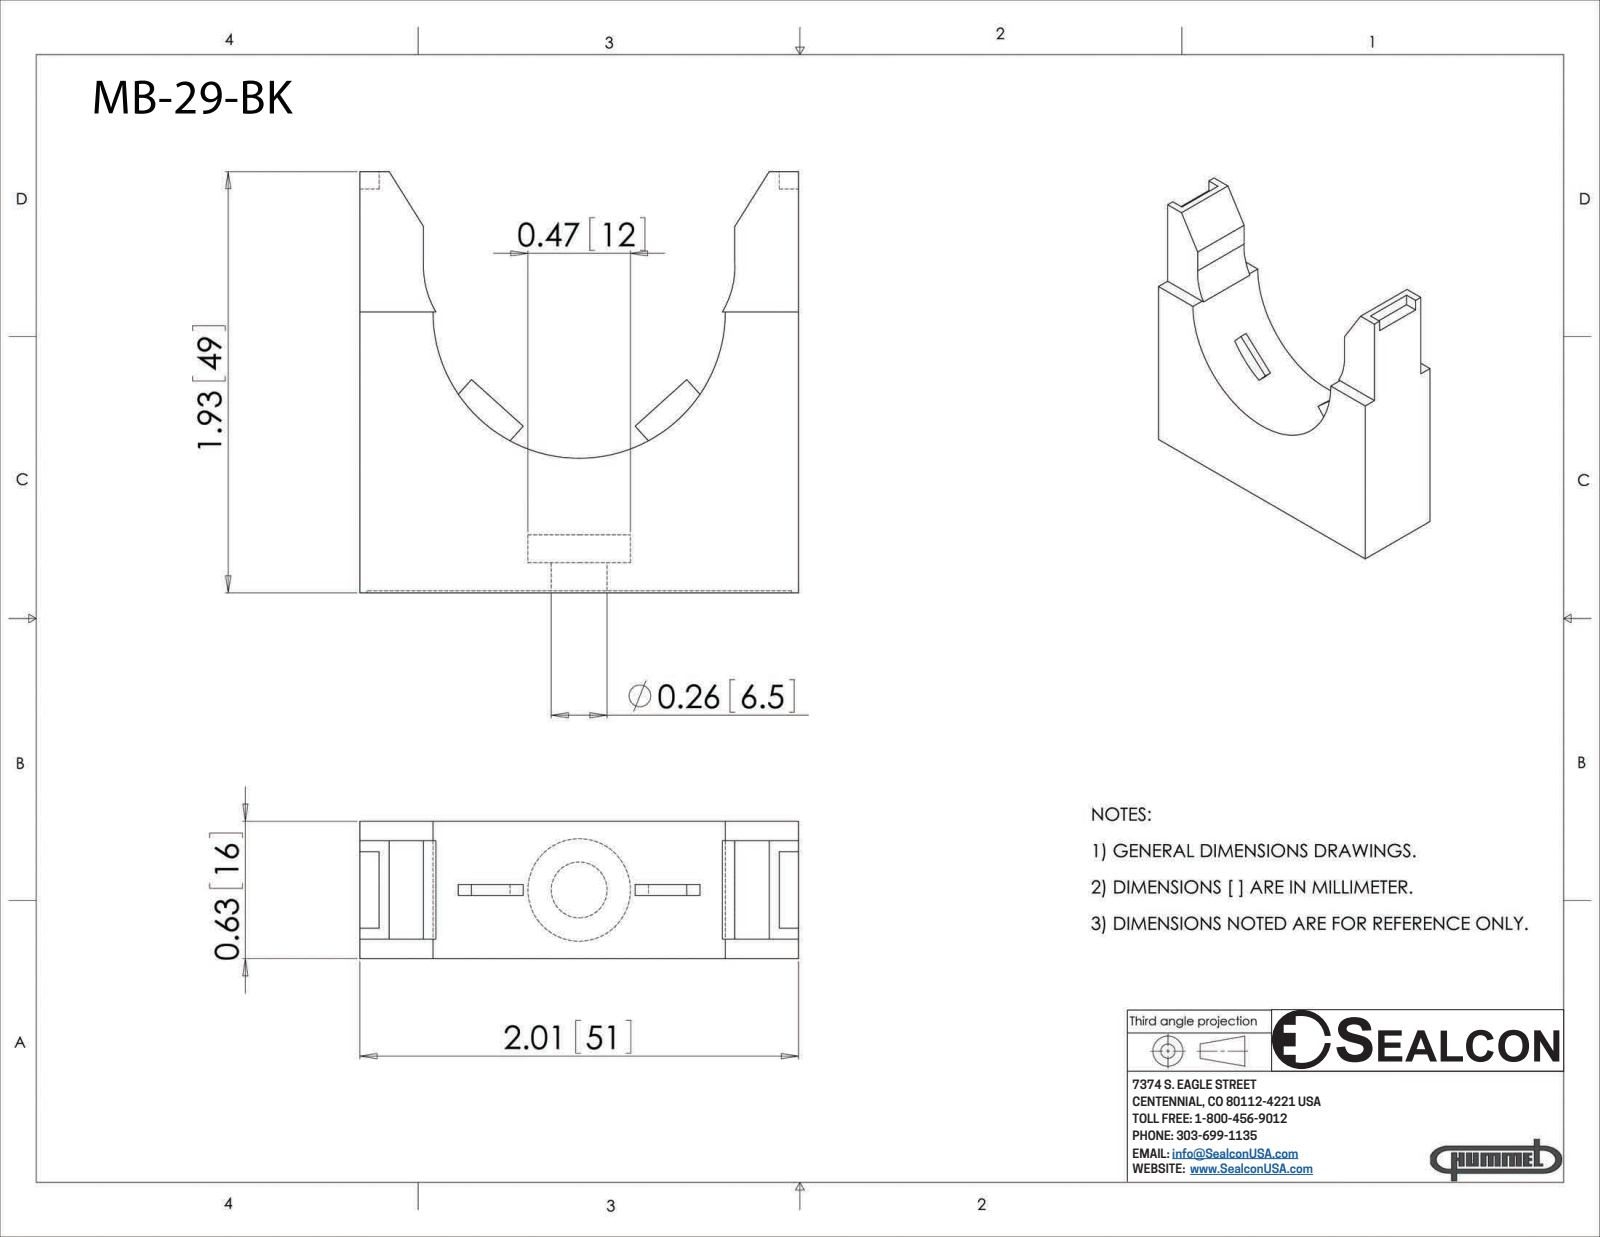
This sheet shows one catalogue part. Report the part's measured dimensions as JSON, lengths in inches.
{"part_name": "MB-29-BK", "step_written_by": "SolidWorks 2008 (CONFIG_CONTROL_DESIGN)", "units": "inches", "bodies": {"solids": 1, "faces": 54, "planar": 46, "cylindrical": 8, "other": 0}, "overall_size": [2.01, 1.93, 0.63], "volume_in3": 1.298, "surface_area_in2": 10.89, "round_holes": [[0.256, 1], [0.47, 1]], "partial_cylinders_radius": [[0.413, 2], [0.67, 1]], "face_to_face_distances": [0.63, 2.01, 0.089, 0.541, 0.451, 0.256, 0.266, 0.292, 1.718, 1.287]}
